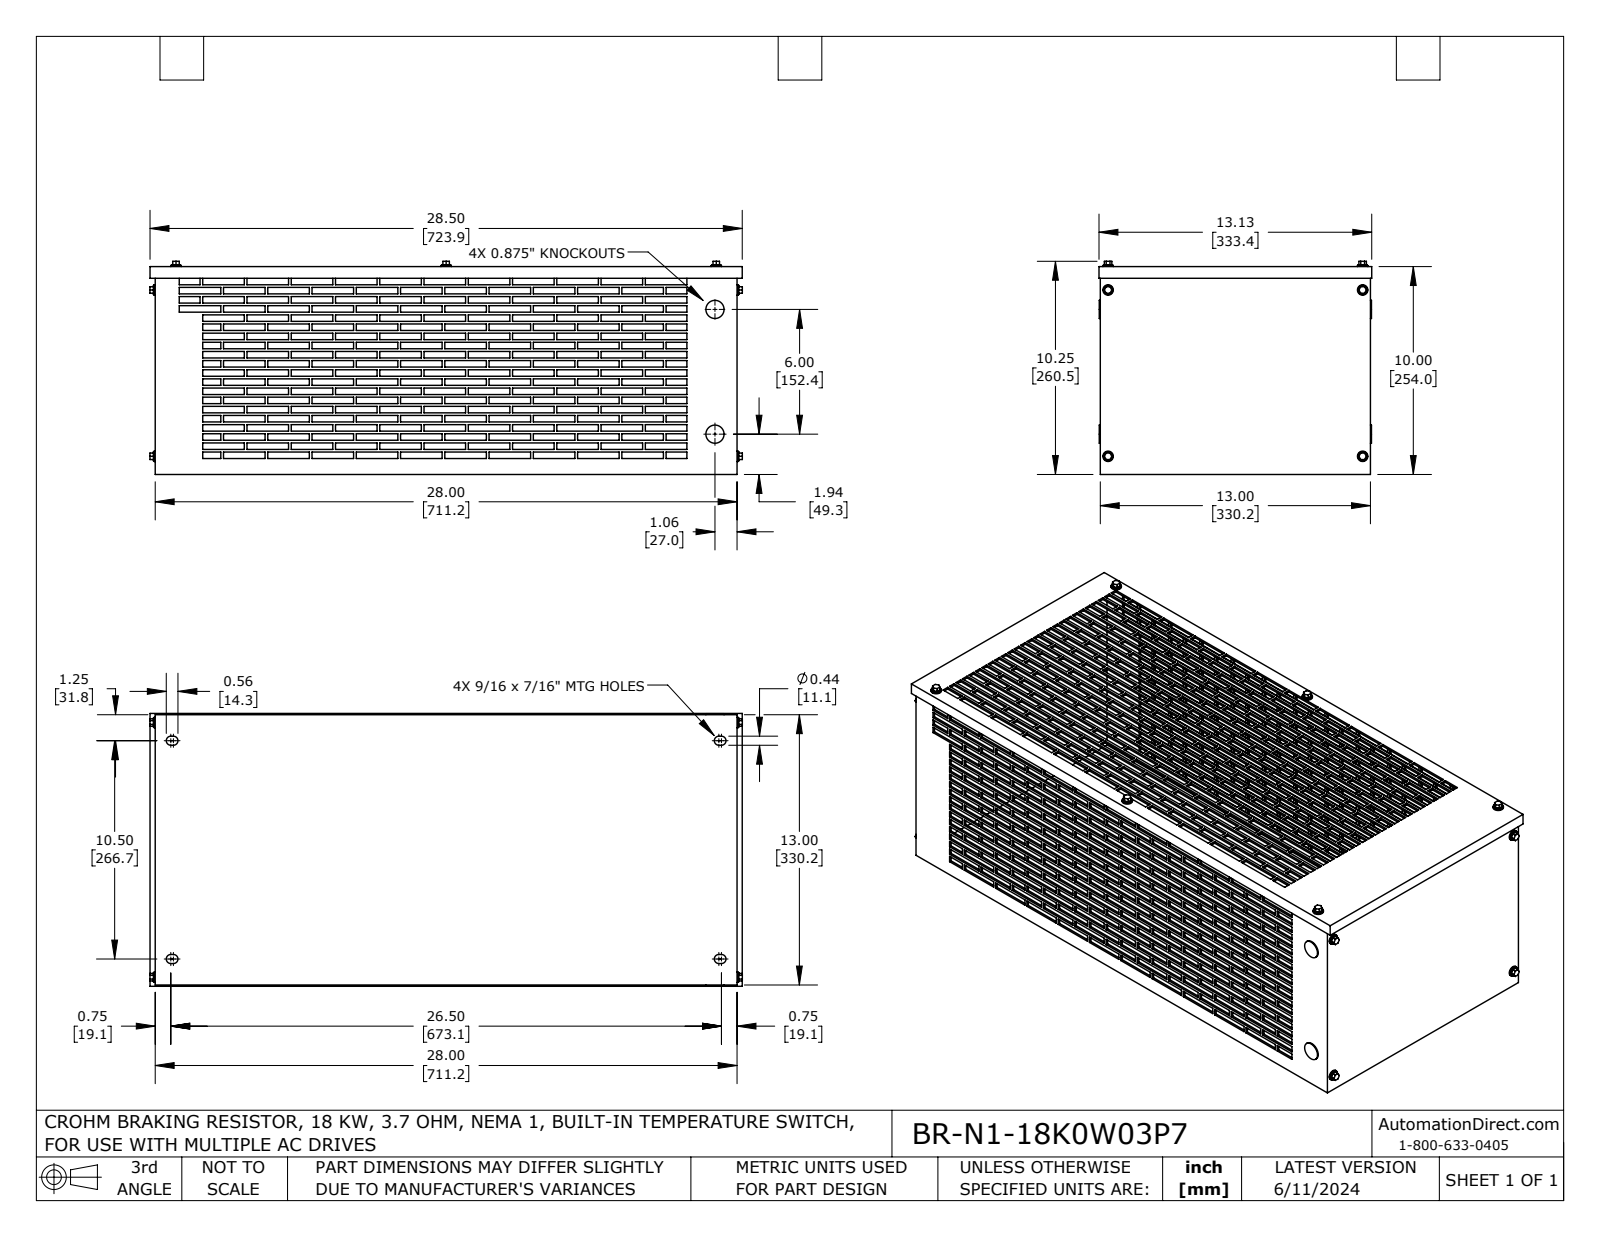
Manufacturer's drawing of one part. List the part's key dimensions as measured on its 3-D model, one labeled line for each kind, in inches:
Part name (STEP PRODUCT): BR-N1-18K0W03P7
STEP written by: SolidWorks 2021 (AUTOMOTIVE_DESIGN)
Units: inches
Bodies: 29 solids, 3342 faces (3250 planar, 92 cylindrical, 0 other)
Overall size (bounding box): 28.509 × 17.629 × 13.125
Volume: 108.9 in³ · Surface area: 2 532 in²
Round holes (diameter × count): ⌀0.25 ×8, ⌀0.75 ×2
Round bosses / shafts (diameter × count): ⌀0.5 ×10, ⌀0.437 ×10, ⌀0.875 ×2
Partial cylindrical surfaces — rounded edges, fillets, slot ends (radius × count): R0.219 ×8
Main face-to-face distances: 0.1, 9.9, 12.9, 27.9, 10, 9.8, 13, 12.8, 28, 27.8
Hole centre spacings: 12.25, 13, 17.862, 26, 28.741, 6
